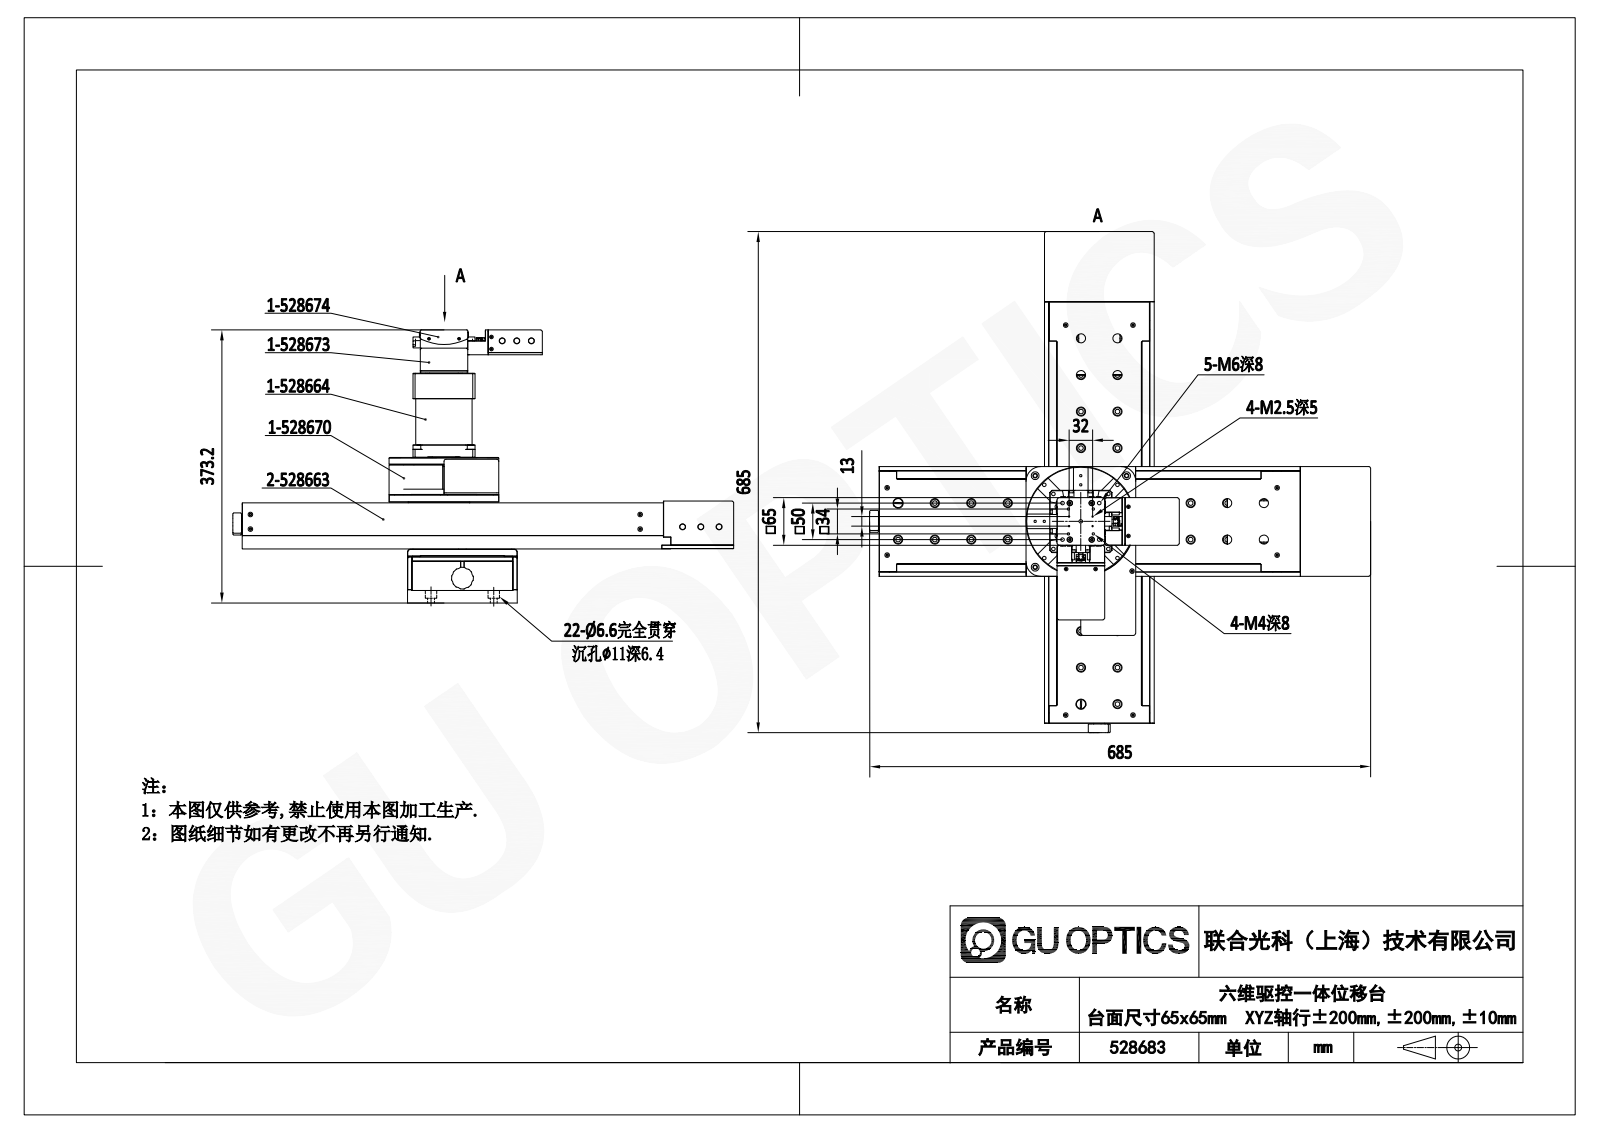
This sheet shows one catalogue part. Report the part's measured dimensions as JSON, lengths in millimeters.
{"part_name": "528683; 528674; 528664; 528673 (+2 more)", "step_written_by": "SolidWorks 2020 (CONFIG_CONTROL_DESIGN)", "units": "millimeters", "bodies": {"solids": 227, "faces": 9501, "planar": 5726, "cylindrical": 2287, "other": 1488}, "overall_size": [685, 685, 373.2], "volume_mm3": 8691000, "surface_area_mm2": 2420000, "round_holes": [[5, 102], [3.3, 93], [2.5, 90], [3.4, 86], [11, 75], [6.5, 73], [6.6, 71], [12.5, 44], [8, 38], [4.5, 36], [3.5, 34], [2.46, 32]], "round_bosses_or_shafts": [[2, 36], [4, 20], [3, 18], [7, 16], [7.5, 8], [5.5, 8], [2.5, 8], [2.4, 8]], "partial_cylinders_radius": [[2, 153], [1, 57], [5, 49], [3, 35], [4, 19], [7.5, 18], [2.5, 13], [1.35, 8]], "face_to_face_distances": [74, 6, 57, 18, 39, 63, 45, 17, 144, 150], "hole_center_spacings": [12.5, 62.5, 25, 37.5, 50, 30, 27.95, 39.53]}
